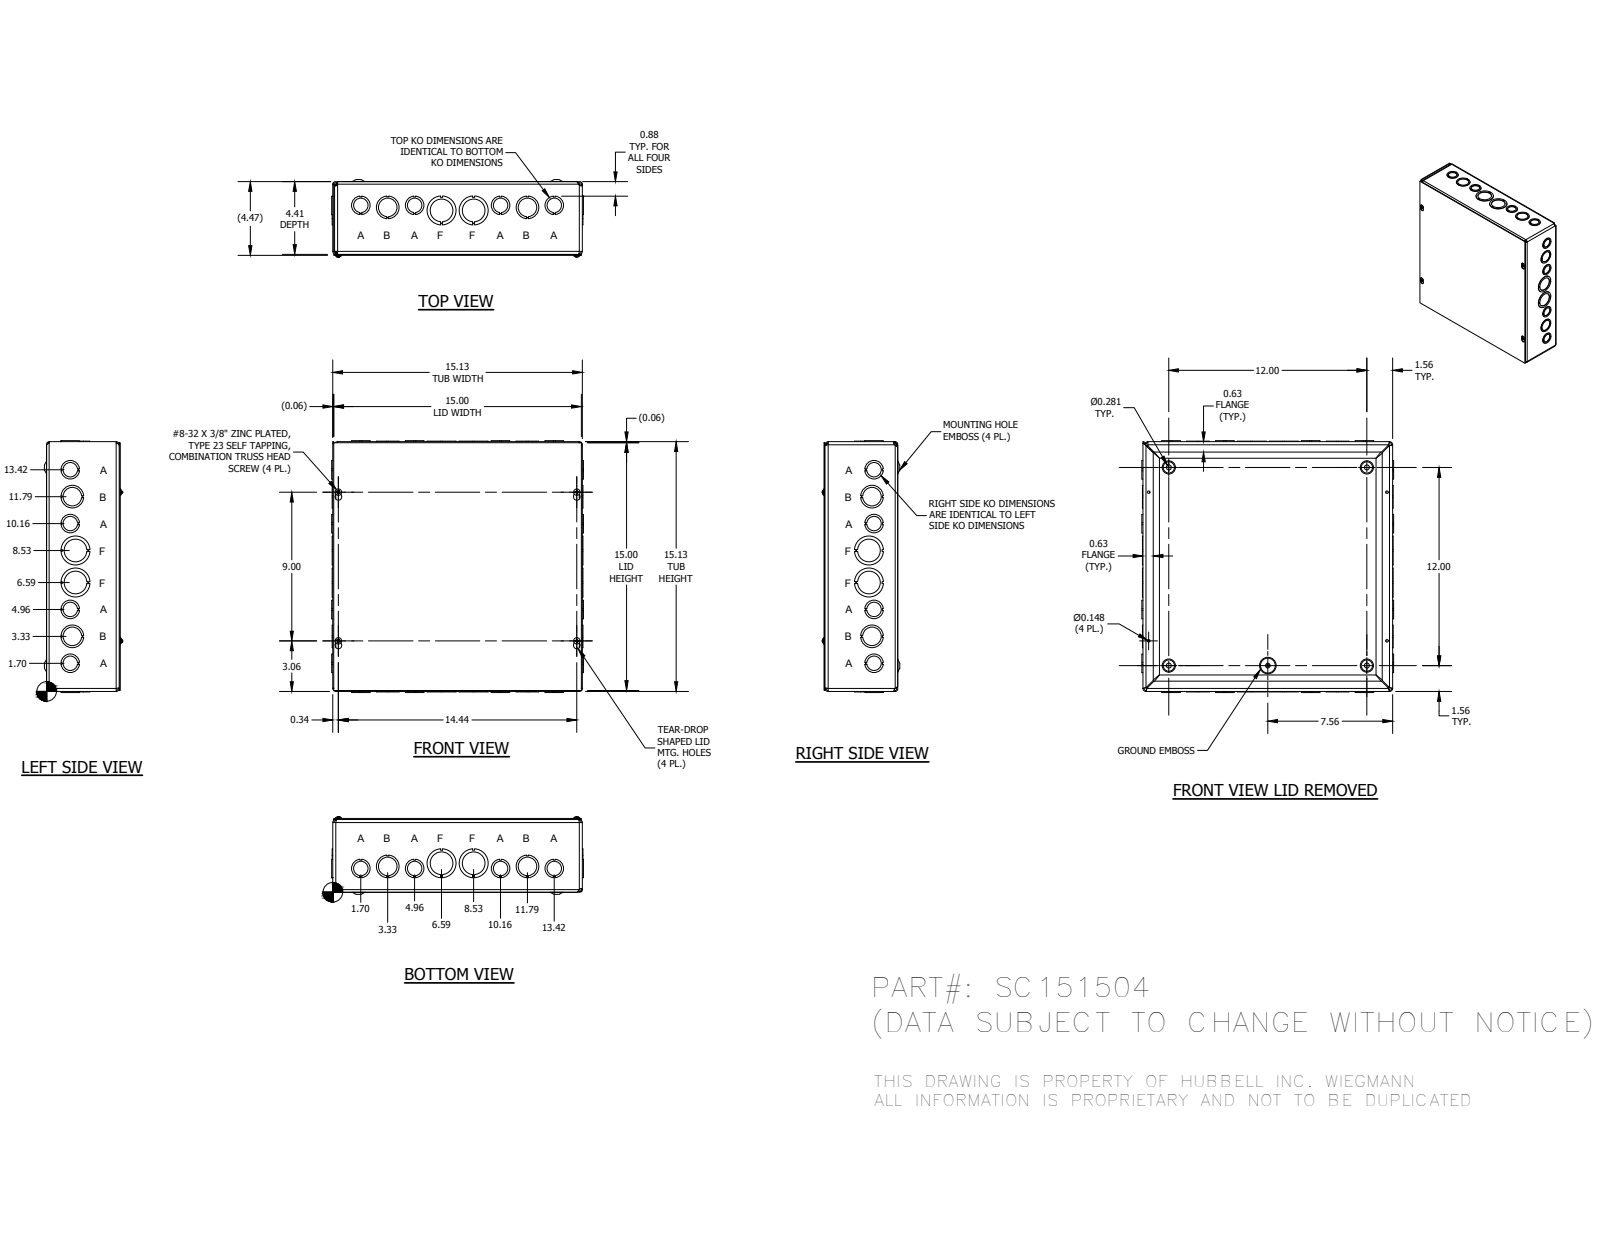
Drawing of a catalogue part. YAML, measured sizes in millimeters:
part_name: "SC1515BKP; SC151504WRA; SC1515LID; 34056 (+1 more)"
step_written_by: "Autodesk Inventor 2014 (AUTOMOTIVE_DESIGN)"
units: millimeters
bodies: {solids: 38, faces: 1254, planar: 837, cylindrical: 259, other: 158}
overall_size: [387.32, 387.32, 119.2]
round_holes:
  - {diameter: 28.57, count: 12}
  - {diameter: 22.22, count: 8}
  - {diameter: 34.92, count: 8}
  - {diameter: 3.76, count: 4}
  - {diameter: 7.62, count: 4}
  - {diameter: 44.45, count: 4}
  - {diameter: 4.19, count: 1}
round_bosses_or_shafts:
  - {diameter: 9.75, count: 4}
  - {diameter: 4.17, count: 4}
  - {diameter: 5.8, count: 1}
partial_cylinders:
  - {radius: 3.17, count: 12}
  - {radius: 4.75, count: 8}
  - {radius: 1.4, count: 4}
  - {radius: 1.57, count: 4}
  - {radius: 2.38, count: 4}
  - {radius: 2.97, count: 4}
  - {radius: 3.15, count: 4}
  - {radius: 3.96, count: 4}
face_to_face_distances: [1.57, 110.32, 382.6, 111.89, 1.59, 111.91, 113.48, 384.17, 381.03, 1.58]
hole_center_spacings: [41.52, 42.15, 49.09, 82.94, 91.03, 132.17, 173.51, 214.88]
